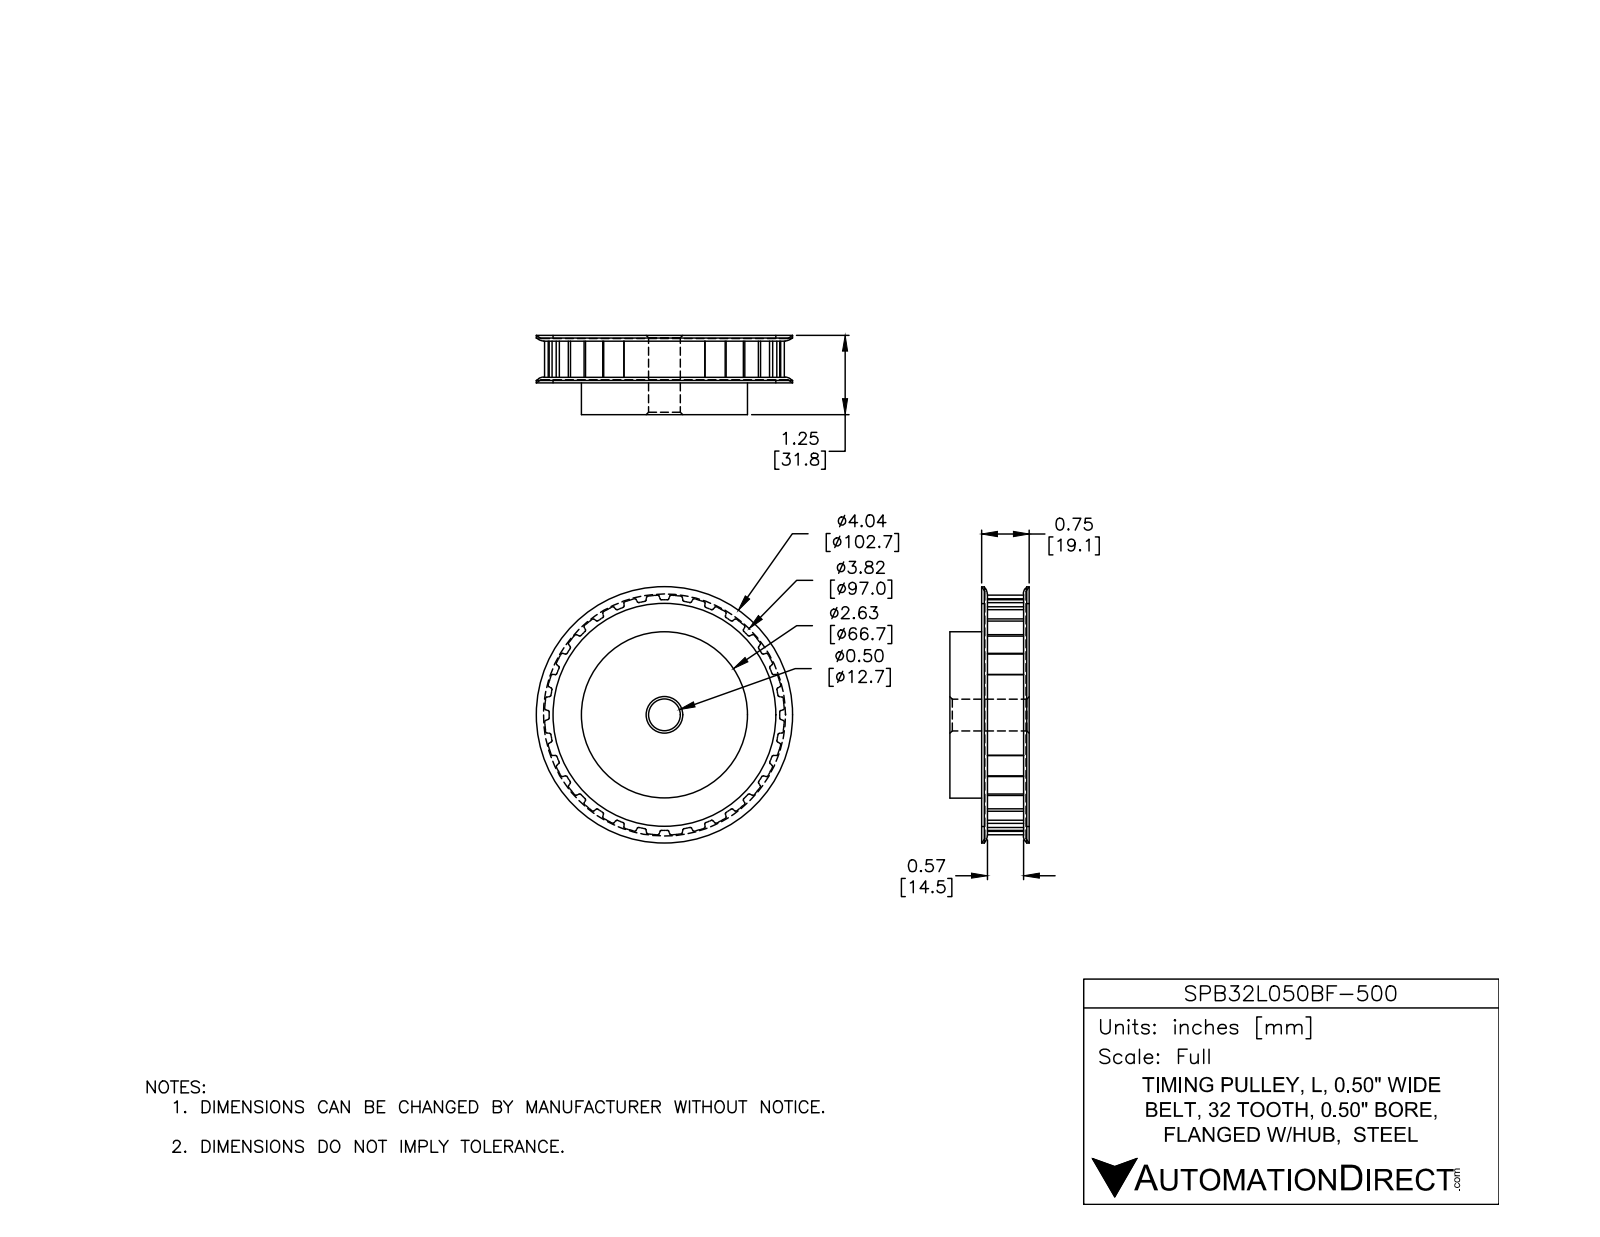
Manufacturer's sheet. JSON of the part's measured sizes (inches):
{"part_name": "SPB32L050BF-500", "step_written_by": "SolidWorks 2015 (AUTOMOTIVE_DESIGN)", "units": "inches", "bodies": {"solids": 1, "faces": 317, "planar": 103, "cylindrical": 198, "other": 16}, "overall_size": [4.044, 4.044, 1.25], "volume_in3": 10.67, "surface_area_in2": 46.4, "round_holes": [[0.5, 1]], "round_bosses_or_shafts": [[4.044, 1], [3.518, 1], [2.625, 1]], "partial_cylinders_radius": [[0.02, 128], [1.895, 1]], "face_to_face_distances": [1.25, 0.05, 0.7, 0.75, 0.5, 0.55, 0.65, 1.2, 0.09, 0.66]}
